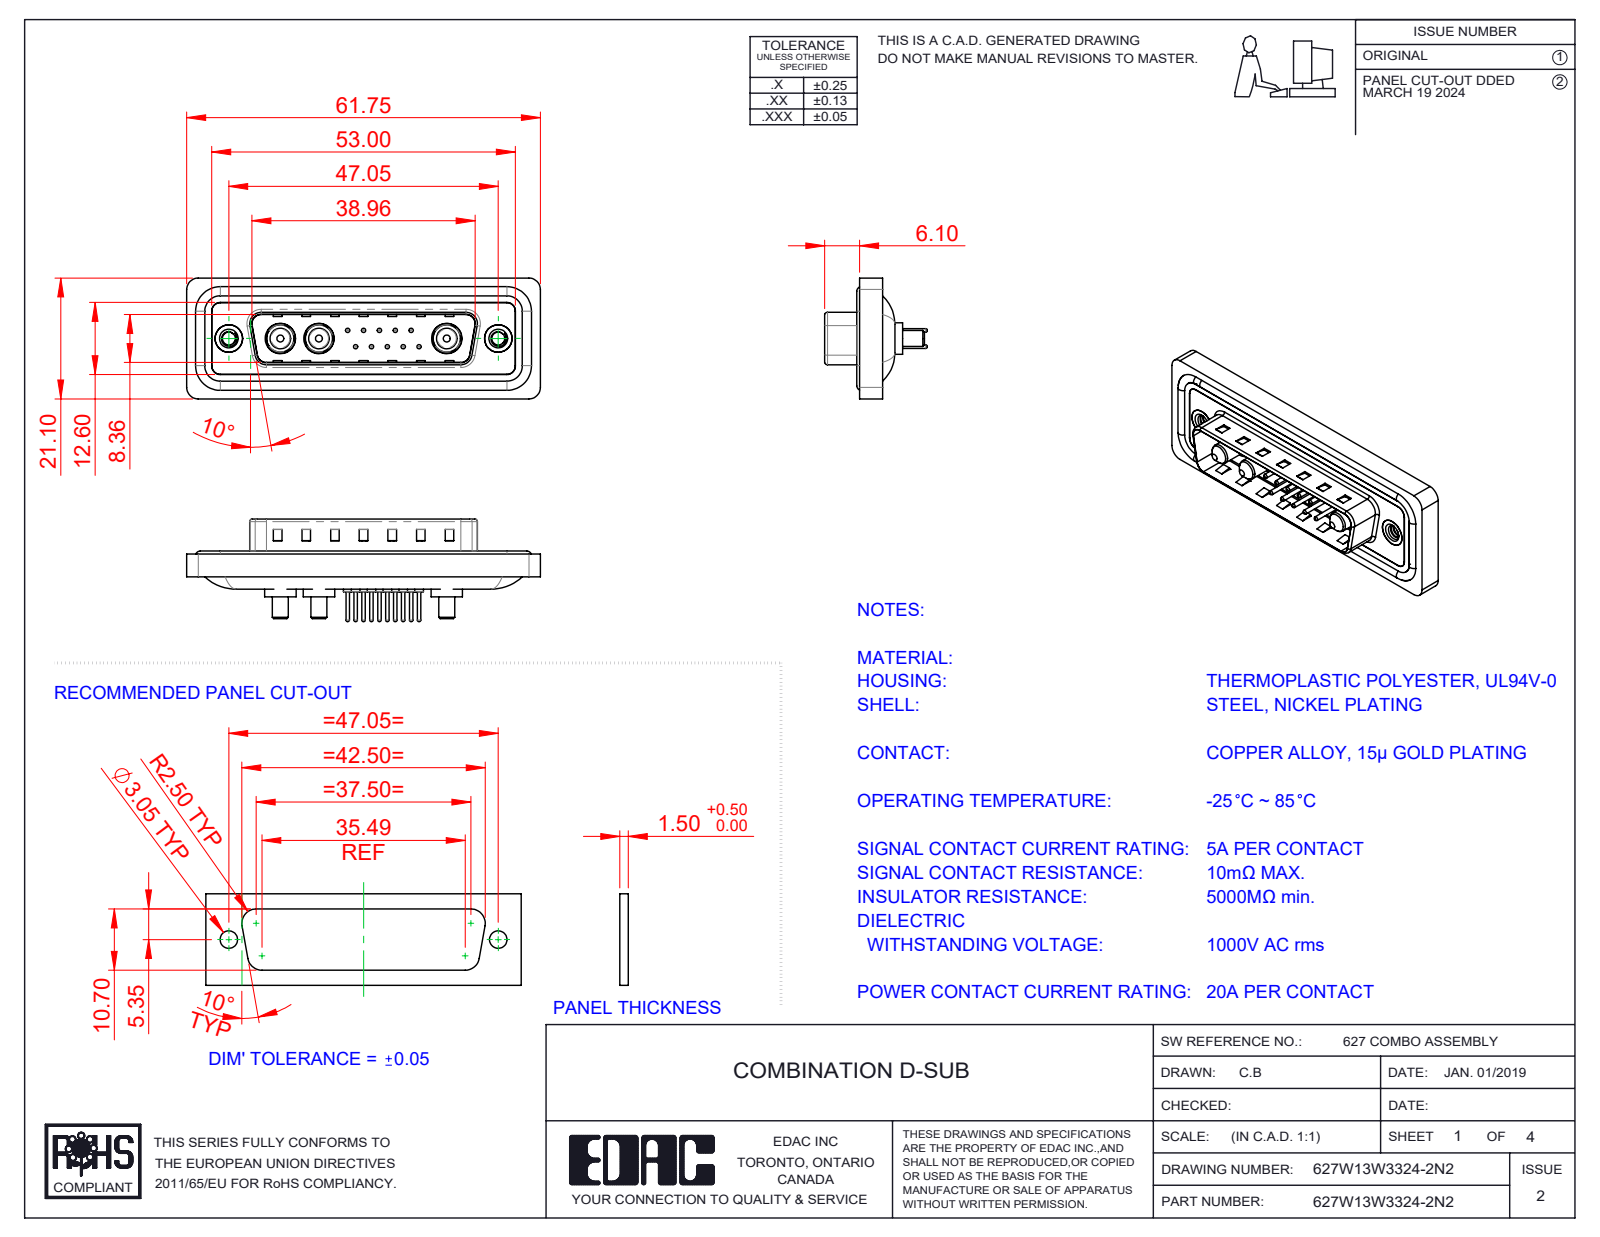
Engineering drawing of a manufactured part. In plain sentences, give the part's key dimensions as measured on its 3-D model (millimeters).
The part is named "627Combo Threaded Rivet_2; 627Combo Waterproof Housing_25 Contacts; 627Combo Housing_13W3; Power Pin_20A S (+5 more)". Its 3-D file was written by "SolidWorks 2023 (CONFIG_CONTROL_DESIGN)". It is 23 solids with 970 faces: 309 planar, 385 cylindrical and 276 other. Overall it measures 61.75 by 21.1 by 17.9 millimeters. Its volume is 7 335 cubic millimeters and its surface area 11 875 square millimeters. Round holes: 10 of diameter 0.75, 10 of diameter 1.6, 10 of diameter 2, 3 of diameter 4.85, 3 of diameter 5.3, 2 of diameter 2.26, 2 of diameter 4, 2 of diameter 4.8, 2 of diameter 5. Round bosses or shafts: 10 of diameter 1.5, 10 of diameter 0.6, 4 of diameter 1.6, 3 of diameter 5.5, 3 of diameter 5.2, 3 of diameter 4.75, 3 of diameter 3.75, 3 of diameter 3.6. Partial cylindrical surfaces (rounded edges, fillets, slot ends): 22 of radius 1.5, 18 of radius 2, 8 of radius 0.5, 8 of radius 1.6, 4 of radius 0.25, 4 of radius 0.6, 4 of radius 0.65, 4 of radius 0.9. The main face-to-face distances are 0.4, 1.5, 1.1, 1.6, 0.5, 3.1, 2.9, 0.82, 9.58, 4.1. The hole center spacings are 3.16, 2.77, 5.04, 5.54, 7.49, 5.03, 8.31, 10.11.
